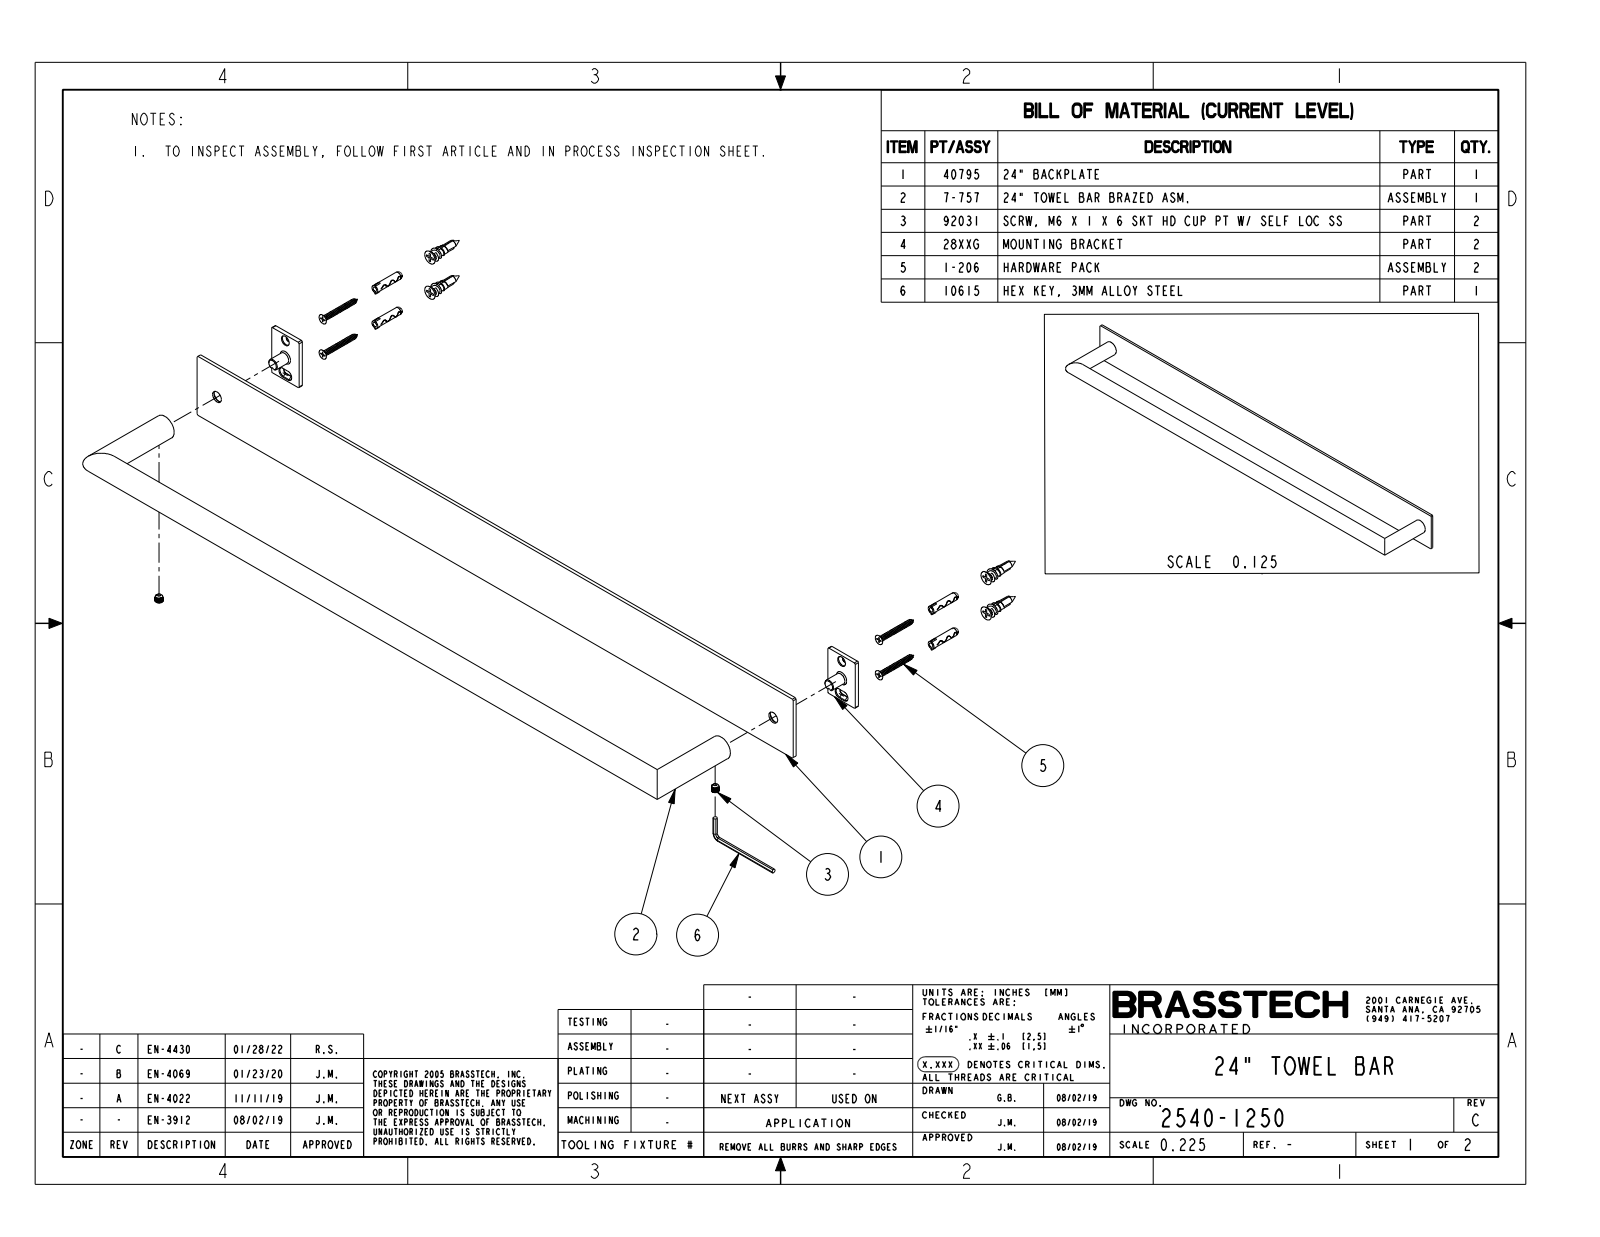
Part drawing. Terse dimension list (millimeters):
name: 2803
written by: CREO PARAMETRIC BY PTC INC, 2018400 (CONFIG_CONTROL_DESIGN)
unit: mm
bodies: 1 solid, 70 faces (26 planar, 26 cylindrical, 18 other)
size: 653.6 × 86.6 × 56
volume: 356 900 mm³; area: 125 400 mm²
bosses: 3× ⌀20.1, 3× ⌀12.7, 3× ⌀11.5
rounds: 8× R1
face distances: 3, 3.5, 6.5, 56, 6.5, 49.5, 7, 37, 616.6, 646.6
